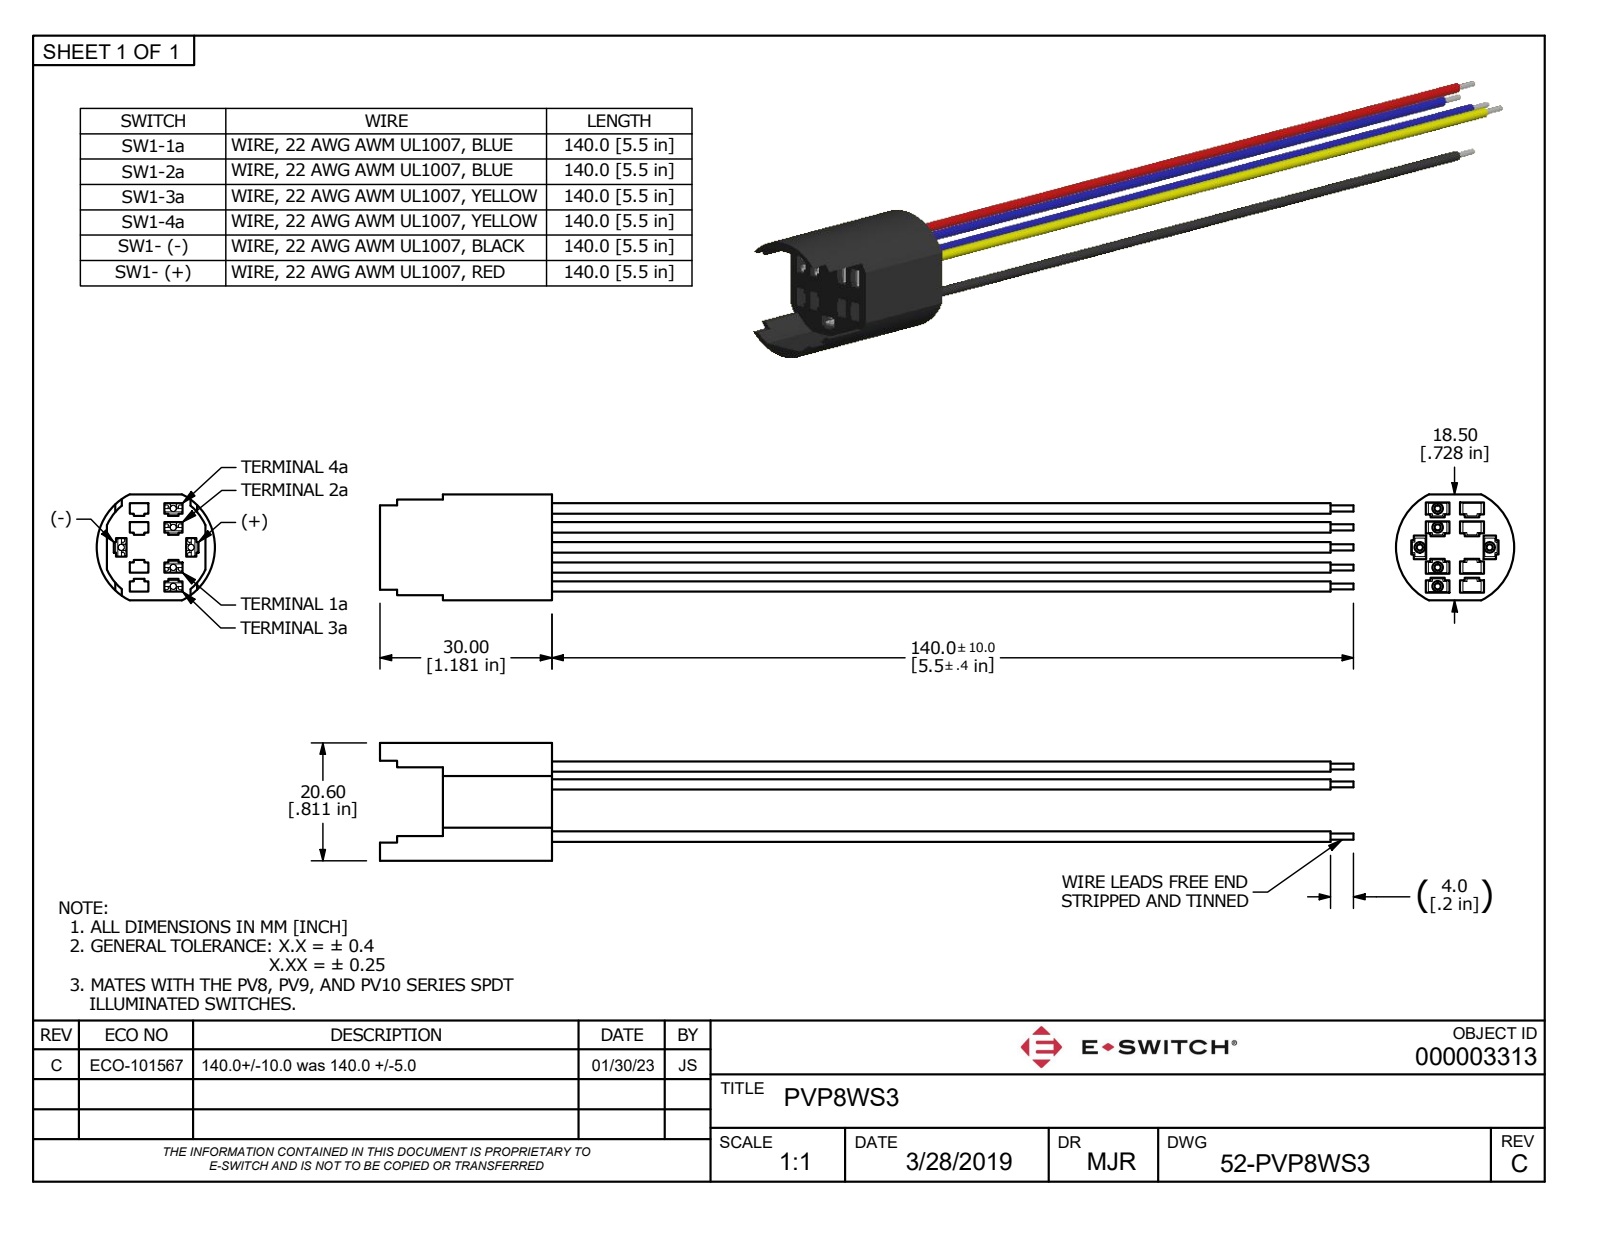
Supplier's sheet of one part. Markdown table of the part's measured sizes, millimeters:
| quantity | value |
| --- | --- |
| part name | PVP8WS3 |
| STEP written by | Autodesk Inventor 2018 (AP242_MANAGED_MODEL_BASED_3D_ENGINEERING_MIM_LF) |
| units | millimeters |
| bodies | 1 solid, 454 faces (346 planar, 72 cylindrical, 36 other) |
| overall size | 170 × 20.6 × 18.5 |
| volume | 7 376 mm³ |
| surface area | 10 177 mm² |
| round bosses / shafts (diameter × count) | 1.8 × 6 |
| partial cylindrical surfaces (radius × count) | 0.25 × 36, 0.5 × 12, 0.52 × 6, 9.45 × 1, 10.3 × 1 |
| main face-to-face distances | 3.3, 12.27, 19, 13.2, 2.2, 2.37, 6.48, 18.5, 10.07, 9.9 |
